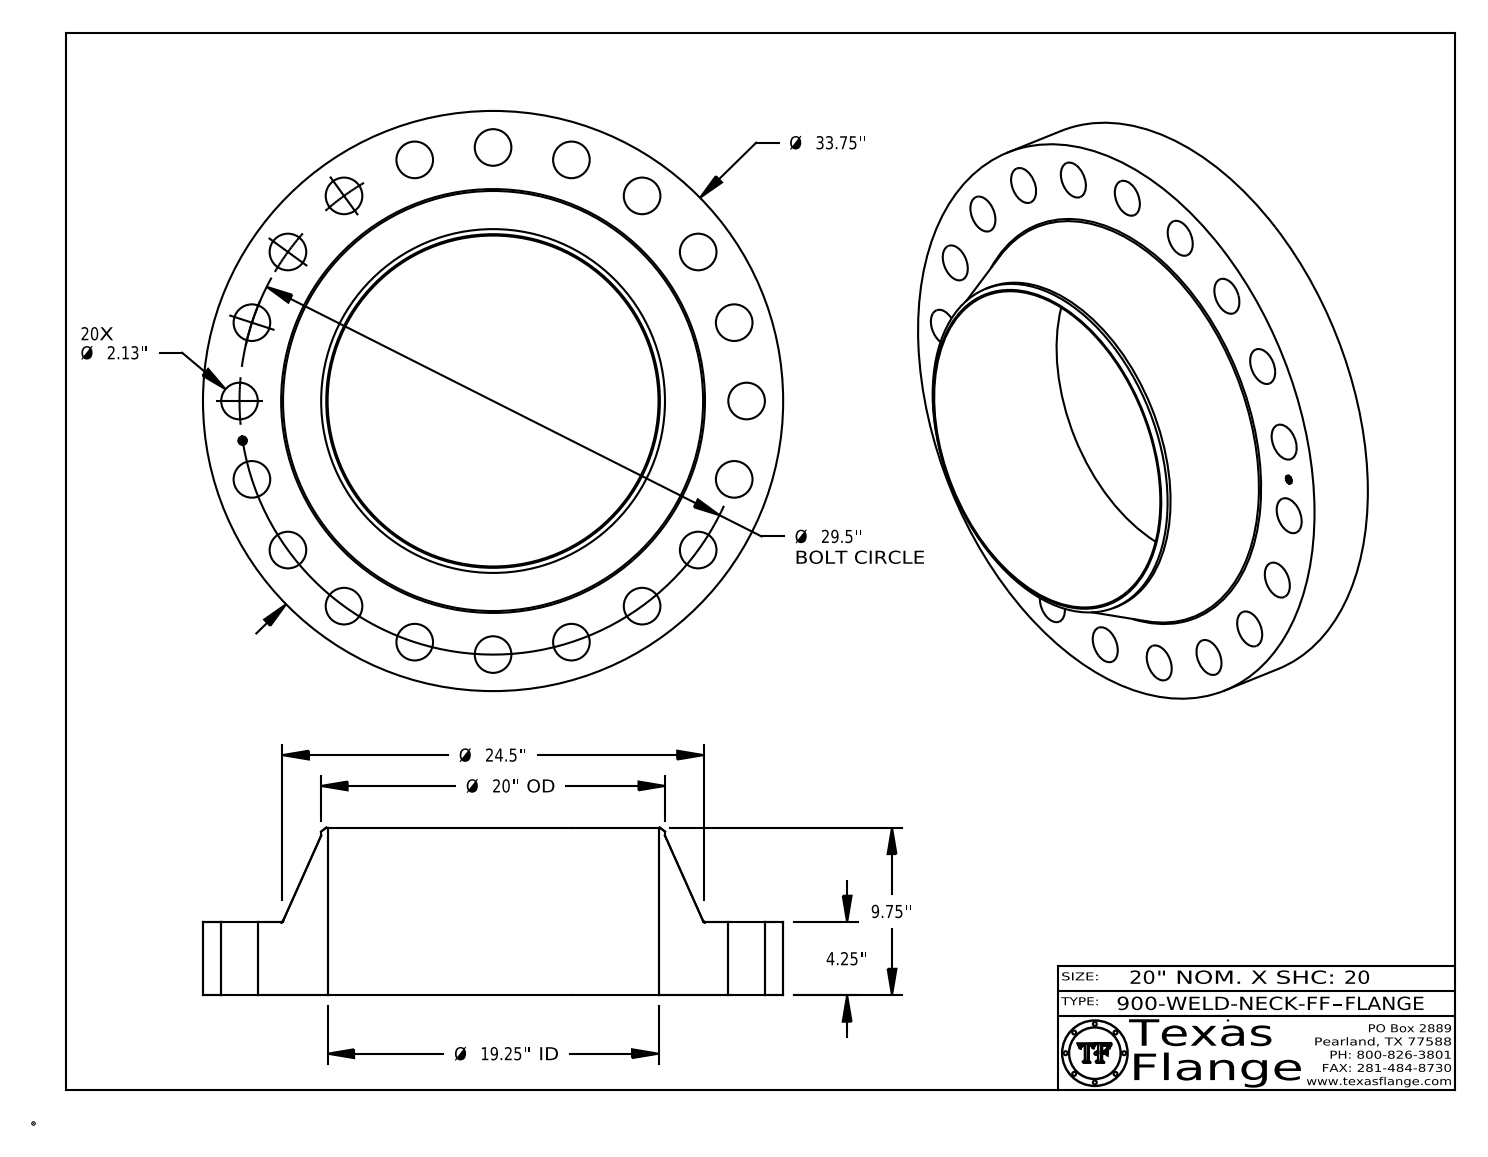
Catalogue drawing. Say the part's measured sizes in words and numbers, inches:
The part is named "900-WELD-NECK-FF". Its 3-D file was written by "CATIA V5 STEP AP214 (AUTOMOTIVE_DESIGN)". It is 1 solid with 440 faces: 368 planar, 66 cylindrical and 6 other. Overall it measures 33.75 by 33.75 by 9.75 inches. Its volume is 2 770 cubic inches and its surface area 2 920 square inches. Round holes: 20 of diameter 2.13, 1 of diameter 0.495, 1 of diameter 19.25. Round bosses or shafts: 8 of diameter 0.03, 1 of diameter 33.75, 1 of diameter 20, 1 of diameter 0.39. The main face-to-face distances are 4.25, 9.75, 5.5, 4.235, 0.015, 5.515, 0.148, 0.145, 0.027, 0.096. The hole center spacings are 14.75, 29.137, 4.615, 17.34, 20.859, 23.866, 26.285, 9.116.
